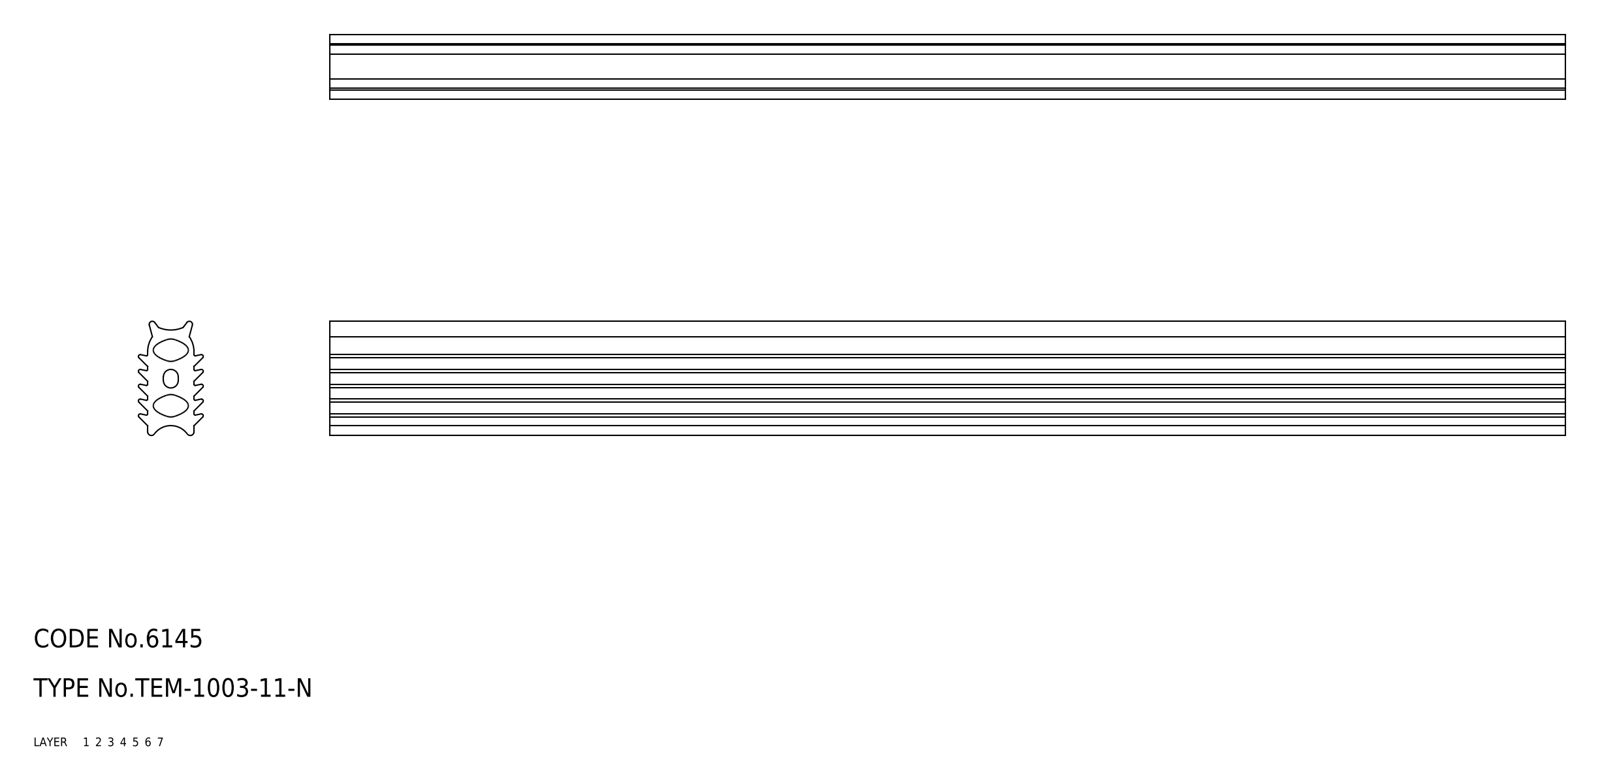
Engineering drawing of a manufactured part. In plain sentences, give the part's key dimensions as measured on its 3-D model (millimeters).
The part is named "gasket". Its 3-D file was written by "CADfix (AUTOMOTIVE_DESIGN)". It is 1 solid with 142 faces: 0 planar, 0 cylindrical and 142 other. Overall it measures 200 by 18.5 by 10.5 millimeters. Its volume is 20 630 cubic millimeters and its surface area 22 540 square millimeters.
